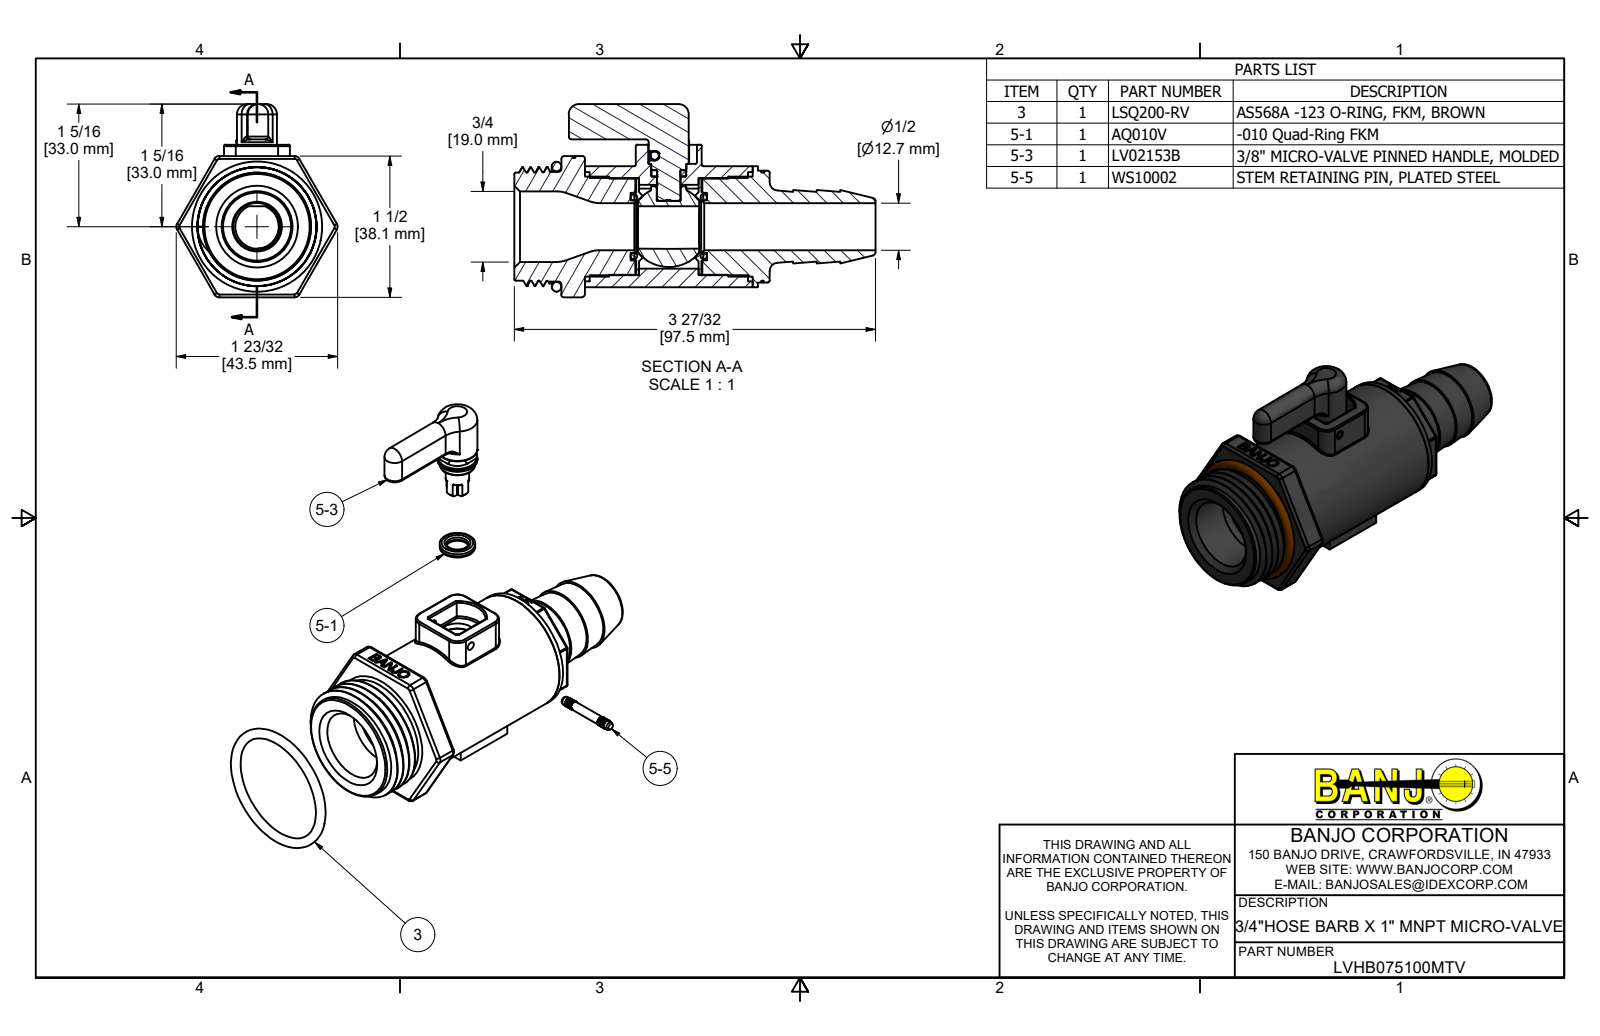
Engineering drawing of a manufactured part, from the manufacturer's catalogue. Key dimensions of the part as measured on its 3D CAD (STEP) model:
Part name (STEP PRODUCT): LVHB075100MTV; LV050SUBV; LV05254A; LV02153B (+8 more)
STEP written by: Autodesk Inventor 2022 (AUTOMOTIVE_DESIGN)
Units: inches
Bodies: 13 solids, 1582 faces (1220 planar, 127 cylindrical, 235 other)
Overall size (bounding box): 3.837 × 2.051 × 1.714
Volume: 3.334 in³ · Surface area: 48.56 in²
Round holes (diameter × count): ⌀0.093 ×1, ⌀0.251 ×1, ⌀0.366 ×1, ⌀0.376 ×1, ⌀0.47 ×1, ⌀0.5 ×1, ⌀0.541 ×1, ⌀0.718 ×1, ⌀0.75 ×1, ⌀0.89 ×1, ⌀1.034 ×1, ⌀1.16 ×1
Round bosses / shafts (diameter × count): ⌀1.285 ×1, ⌀1.165 ×1, ⌀1.064 ×1, ⌀1.062 ×1, ⌀1.024 ×1, ⌀1.02 ×1, ⌀0.558 ×1, ⌀0.425 ×1
Partial cylindrical surfaces — rounded edges, fillets, slot ends (radius × count): R0.01 ×16, R0.02 ×16, R0.015 ×14, R0.03 ×14, R0.06 ×6, R0.125 ×4, R0.05 ×2, R0.109 ×2
Main face-to-face distances: 1.207, 0.575, 0.05, 1.247, 0.04, 0.03, 0.545, 1.237, 0.662, 0.535
